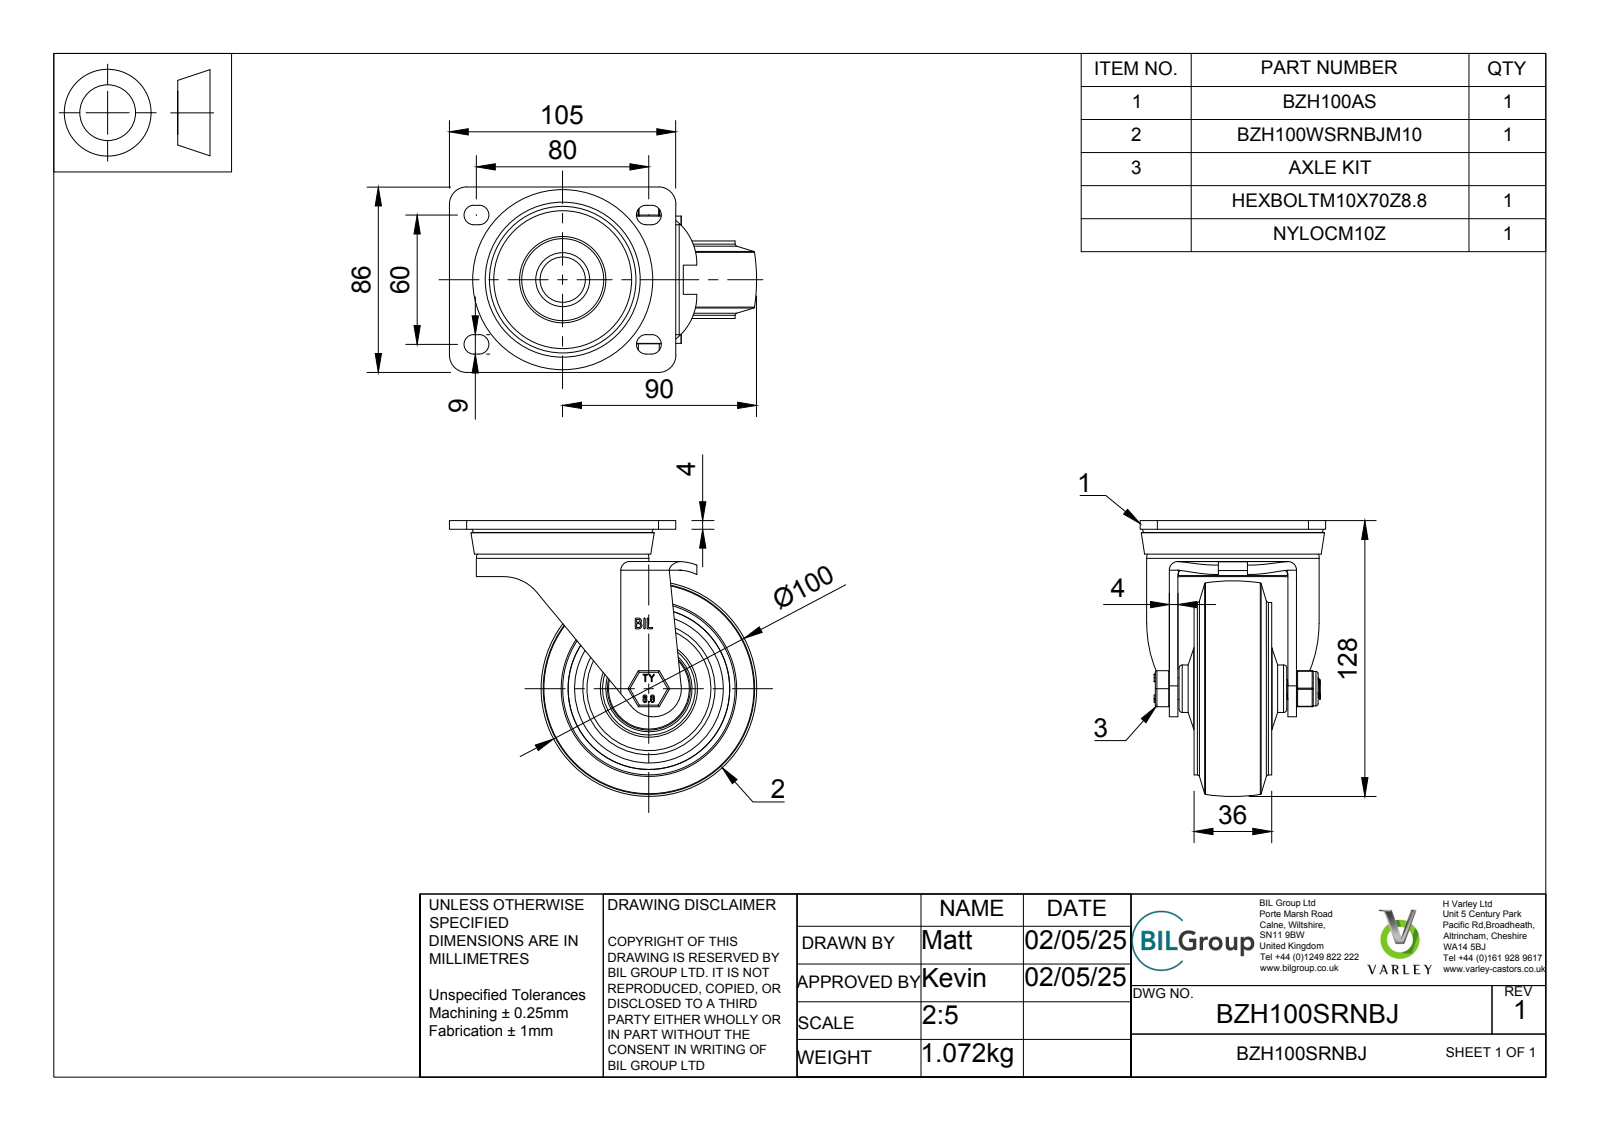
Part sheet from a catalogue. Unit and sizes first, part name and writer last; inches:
Units: inches
Overall size (bounding box): 5.61 × 5.039 × 3.386
Round holes (diameter × count): ⌀1.26 ×2, ⌀0.394 ×1, ⌀0.402 ×1, ⌀0.472 ×1, ⌀0.591 ×1, ⌀0.787 ×1, ⌀0.886 ×1, ⌀0.984 ×1, ⌀1.024 ×1, ⌀1.181 ×1, ⌀1.22 ×1, ⌀1.299 ×1
Round bosses / shafts (diameter × count): ⌀3.15 ×2, ⌀1.988 ×1, ⌀1.693 ×1, ⌀1.516 ×1, ⌀1.378 ×1, ⌀1.22 ×1, ⌀1.201 ×1, ⌀1.102 ×1
Partial cylindrical surfaces — rounded edges, fillets, slot ends (radius × count): R0.02 ×18, R0.177 ×8, R0.03 ×6, R0.079 ×4, R0.315 ×4, R0.157 ×2, R1 ×2, R0.472 ×1
Main face-to-face distances: 0.453, 0.157, 0.295, 2.165, 0.098, 0.591, 0.827, 1.043, 0.551, 1.87
Volume: 19.35 in³ · Surface area: 219.9 in²
Bodies: 23 solids, 774 faces (319 planar, 179 cylindrical, 276 other)
Part name (STEP PRODUCT): BZH100SRNBJ v4; BZH100AS - 2 v1; ZINC PLATED, PRESSED STEEL TOP PLATE (1); ZINC PLATED, PRESSED STEEL FORKS (1) (+8 more)
STEP written by: Autodesk Translation Framework v14.4.0.0 (AUTOMOTIVE_DESIGN)
